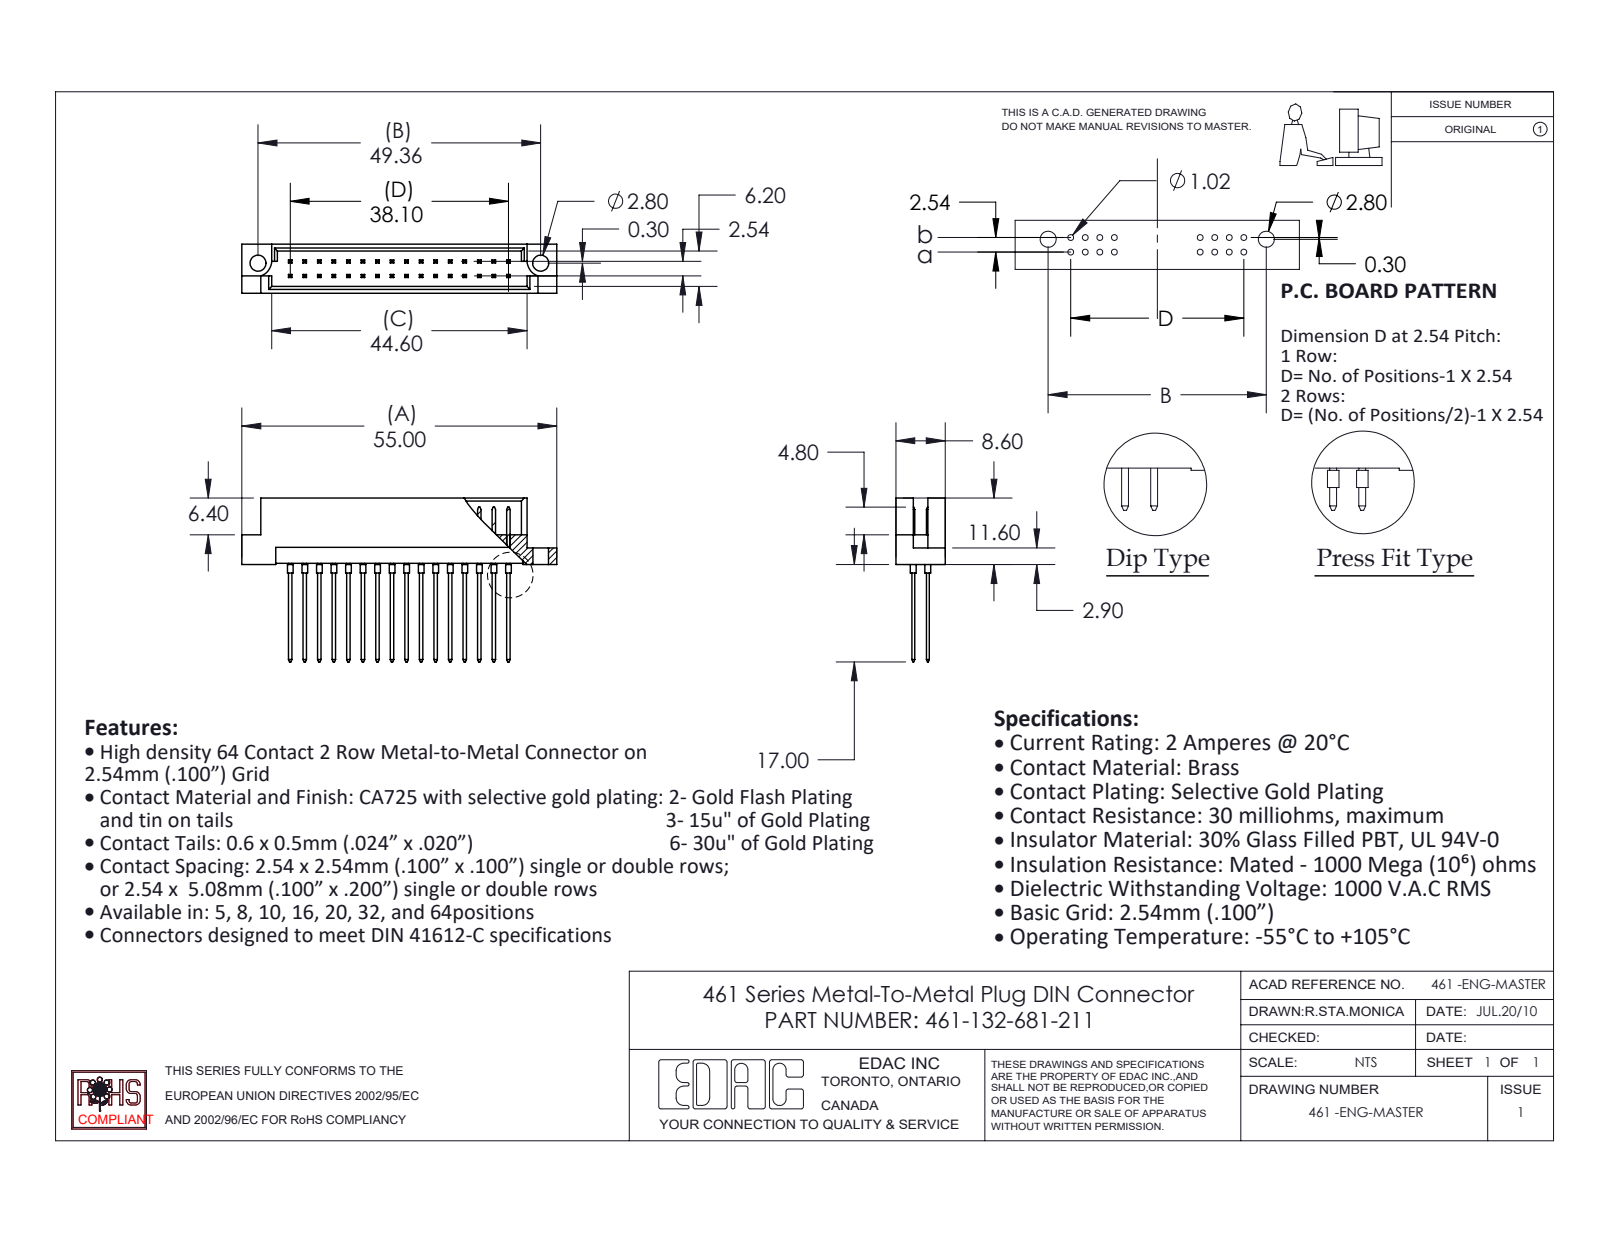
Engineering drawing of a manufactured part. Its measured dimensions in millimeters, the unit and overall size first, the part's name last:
Units: millimetres
Overall size (bounding box): 55 × 28.6 × 8.6
Round holes (diameter × count): ⌀2.8 ×2
Round bosses / shafts (diameter × count): ⌀1 ×32
Partial cylindrical surfaces — rounded edges, fillets, slot ends (radius × count): R2.8 ×2
Main face-to-face distances: 2.54, 1.2, 7.4, 2.78, 5.82, 1.58, 4.62, 3.28, 5.32, 2.08
Hole centre spacings: 49.36
Volume: 2 933 mm³ · Surface area: 5 212 mm²
Bodies: 33 solids, 880 faces (810 planar, 70 cylindrical, 0 other)
Part name (STEP PRODUCT): 461 Part_32; 461-132-681-211; 461-290_81
STEP written by: SolidWorks 2020 (CONFIG_CONTROL_DESIGN)
